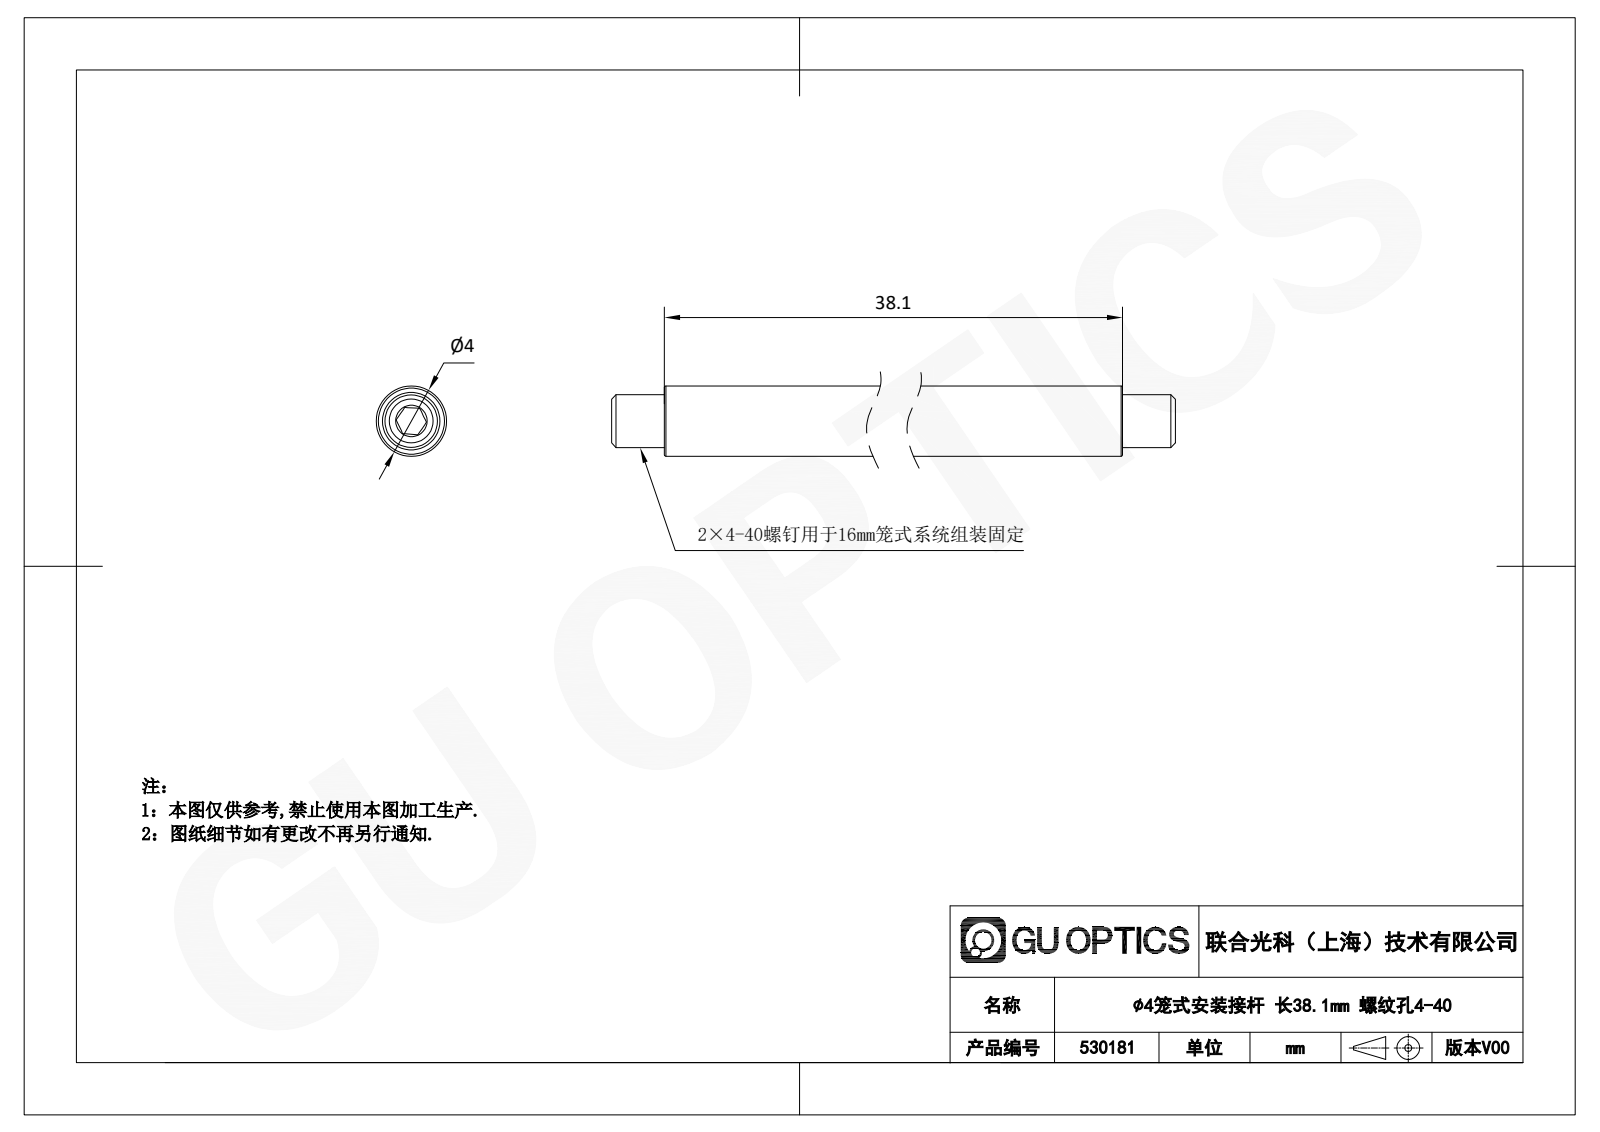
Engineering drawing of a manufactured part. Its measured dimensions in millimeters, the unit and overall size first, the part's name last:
Units: millimetres
Overall size (bounding box): 48.1 × 4 × 4
Round holes (diameter × count): ⌀2.5 ×1
Round bosses / shafts (diameter × count): ⌀4 ×1, ⌀3 ×1
Main face-to-face distances: 3, 35.1, 5, 8, 40.1, 43.1, 1.5, 38.1, 1, 47.1
Volume: 528 mm³ · Surface area: 768 mm²
Bodies: 3 solids, 37 faces (20 planar, 5 cylindrical, 12 other)
Part name (STEP PRODUCT): 530181
STEP written by: SolidWorks 2020 (CONFIG_CONTROL_DESIGN)
